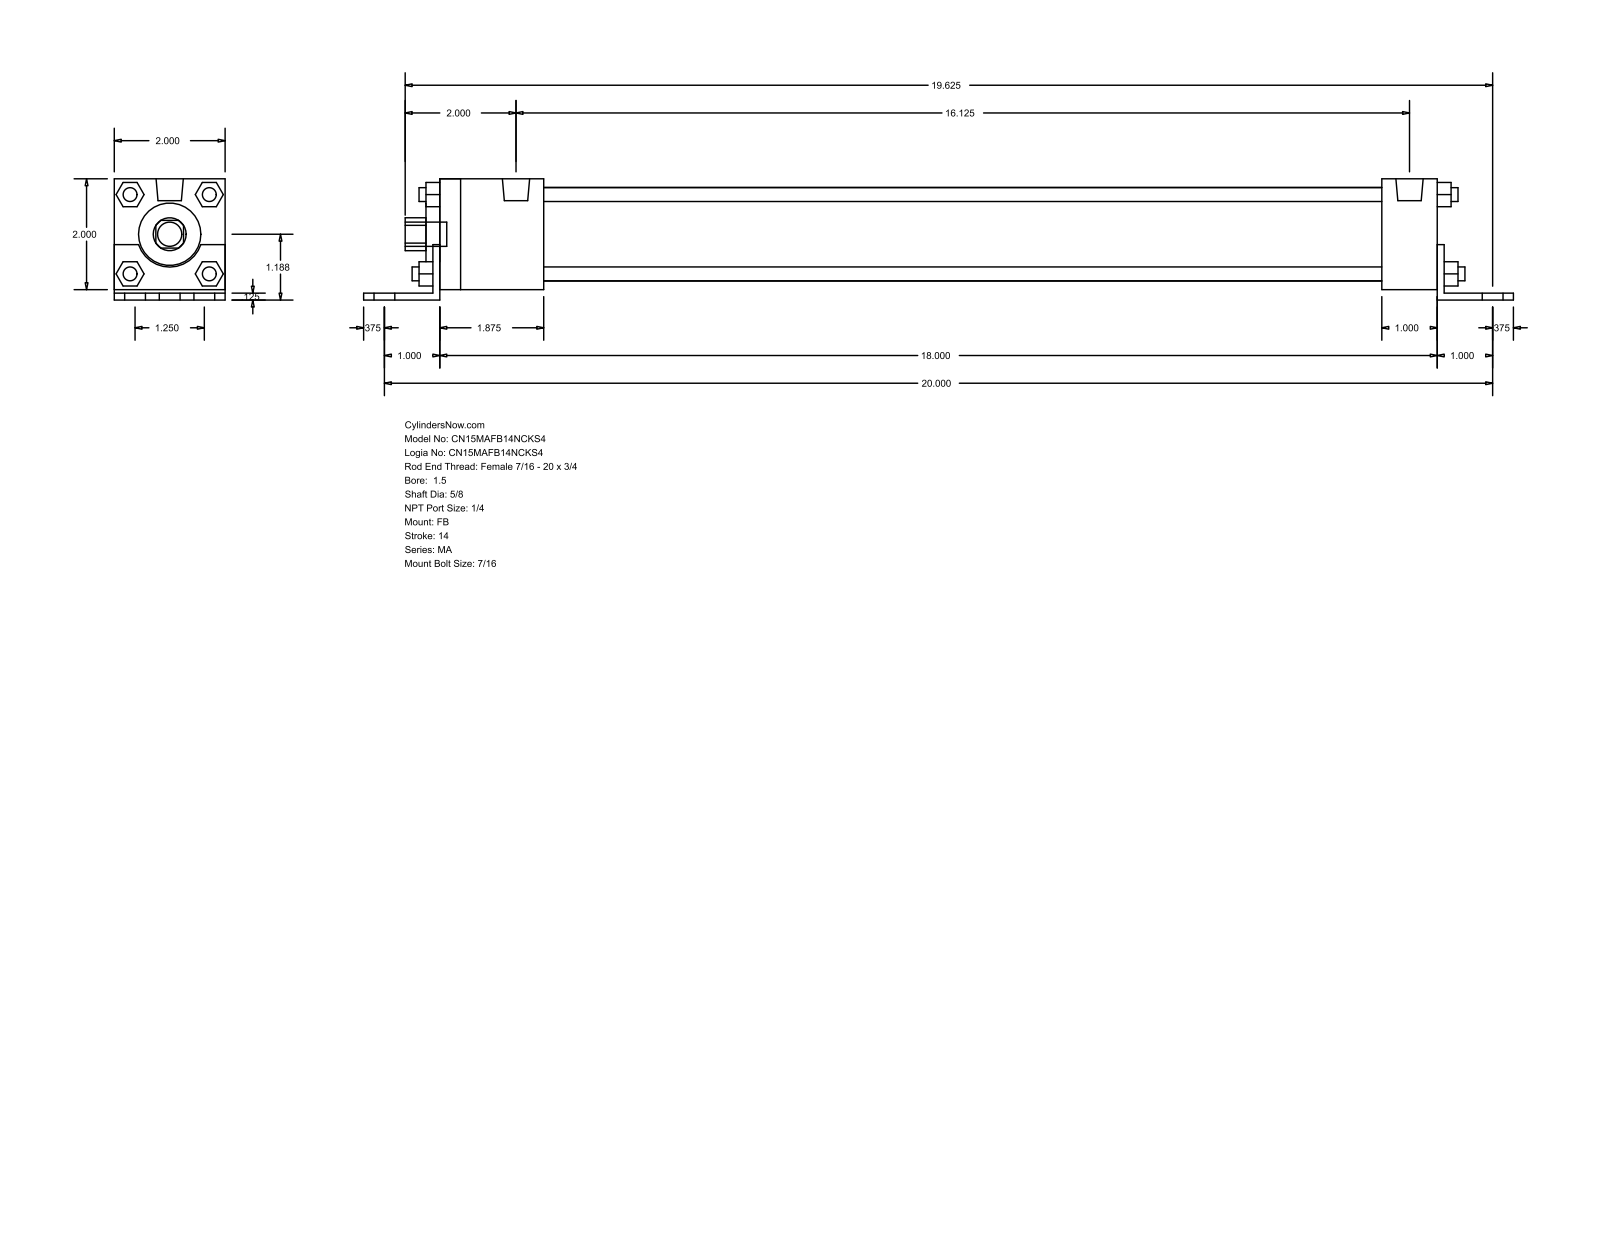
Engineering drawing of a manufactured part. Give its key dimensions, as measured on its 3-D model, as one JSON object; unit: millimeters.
{"part_name": "MA_FB__0150_0.625", "step_written_by": "GSSL Pune (CONFIG_CONTROL_DESIGN)", "units": "millimeters", "bodies": {"solids": 0, "faces": 140, "planar": 105, "cylindrical": 35, "other": 0}, "overall_size": [527.05, 55.56, 50.8], "round_holes": [[15.88, 1], [28.57, 1], [42.93, 1]], "round_bosses_or_shafts": [[11.11, 7], [7.94, 4], [6.35, 4], [12.49, 2]], "partial_cylinders_radius": [[7.54, 1], [15.05, 1]], "face_to_face_distances": [50.8, 3.17, 4.76, 55.56, 1.59, 52.39, 3.18, 460.37, 6.35, 457.19]}
